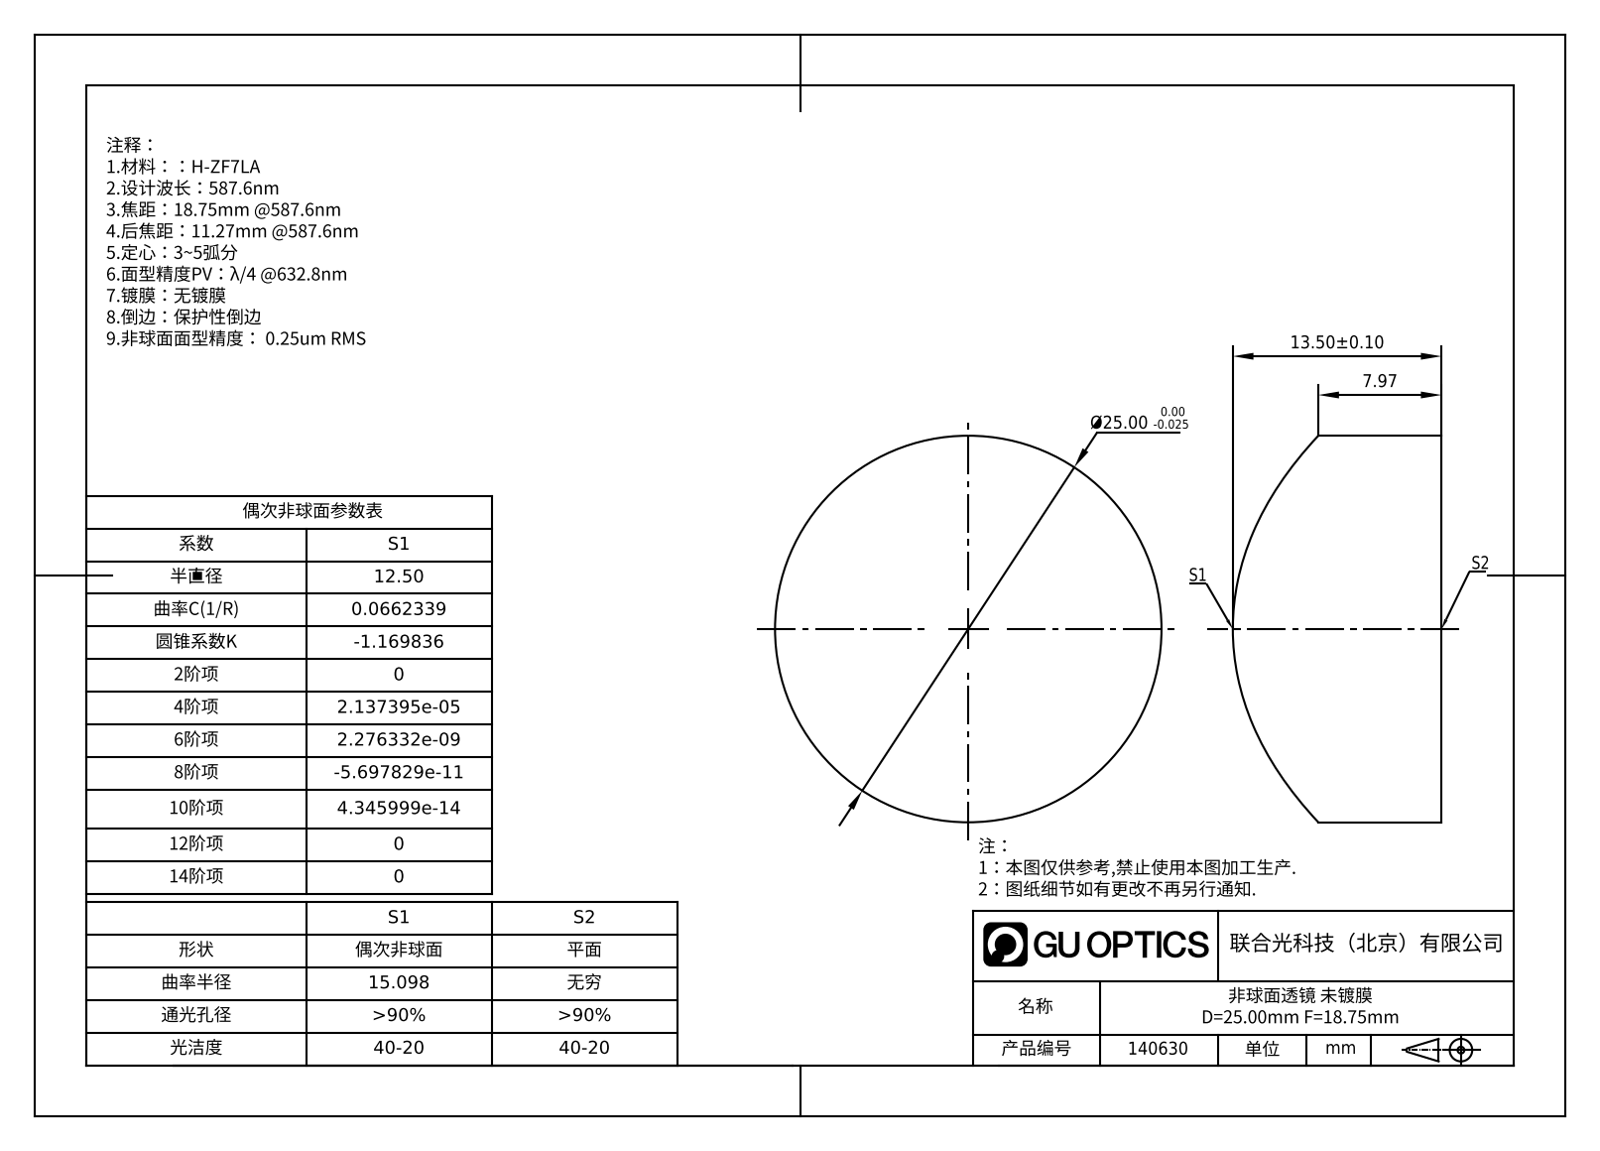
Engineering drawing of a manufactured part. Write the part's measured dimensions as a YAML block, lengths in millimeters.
part_name: "GLA11-025-18.75-H.stp; surfaces 1,2.stp; GLA11-025-18.75-H"
step_written_by: "SolidWorks 2023 (CONFIG_CONTROL_DESIGN)"
units: millimeters
bodies: {solids: 1, faces: 5, planar: 1, cylindrical: 2, other: 2}
overall_size: [25, 25, 13.5]
volume: 5297
surface_area: 1697
round_bosses_or_shafts:
  - {diameter: 25, count: 1}
